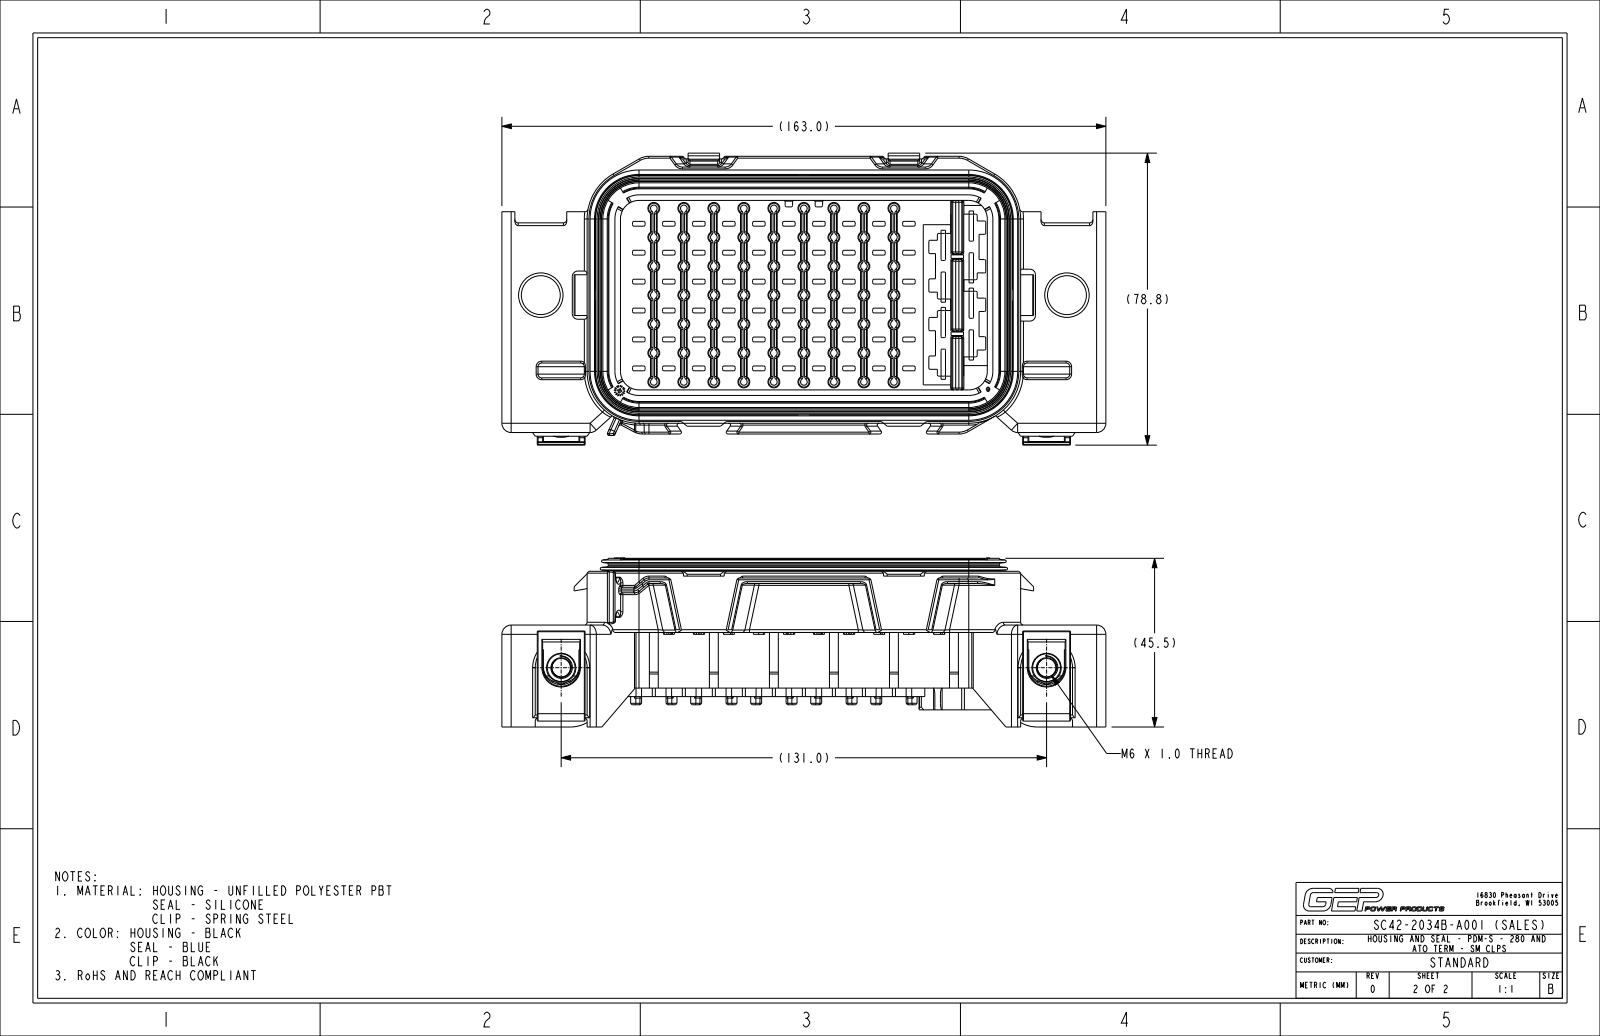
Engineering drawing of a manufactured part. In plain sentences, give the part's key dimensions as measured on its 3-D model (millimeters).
The part is named "SC42-2034B-A001_NCF_SW0001". Its 3-D file was written by "CREO PARAMETRIC BY PTC INC, 2024014 (CONFIG_CONTROL_DESIGN)". It is 1 solid with 7800 faces: 2336 planar, 2168 cylindrical and 3296 other. Overall it measures 163 by 78.75 by 45.6 millimeters. Its volume is 168 455 cubic millimeters and its surface area 115 177 square millimeters. Round holes: 60 of diameter 6.7, 8 of diameter 8.5, 4 of diameter 10.5, 2 of diameter 5, 2 of diameter 7.5, 2 of diameter 12.5. Round bosses or shafts: 2 of diameter 7, 1 of diameter 4. Partial cylindrical surfaces (rounded edges, fillets, slot ends): 678 of radius 0.5, 294 of radius 0.4, 84 of radius 0.3, 63 of radius 1.4, 60 of radius 4.45, 52 of radius 0.2, 43 of radius 0.9, 38 of radius 1. The main face-to-face distances are 2, 5.5, 7.5, 1.5, 9, 7, 11.5, 9.5, 1.8, 2.5. The hole center spacings are 17.58, 8.1, 22.49, 16.2, 28.88, 24.3, 15.6, 35.96.
